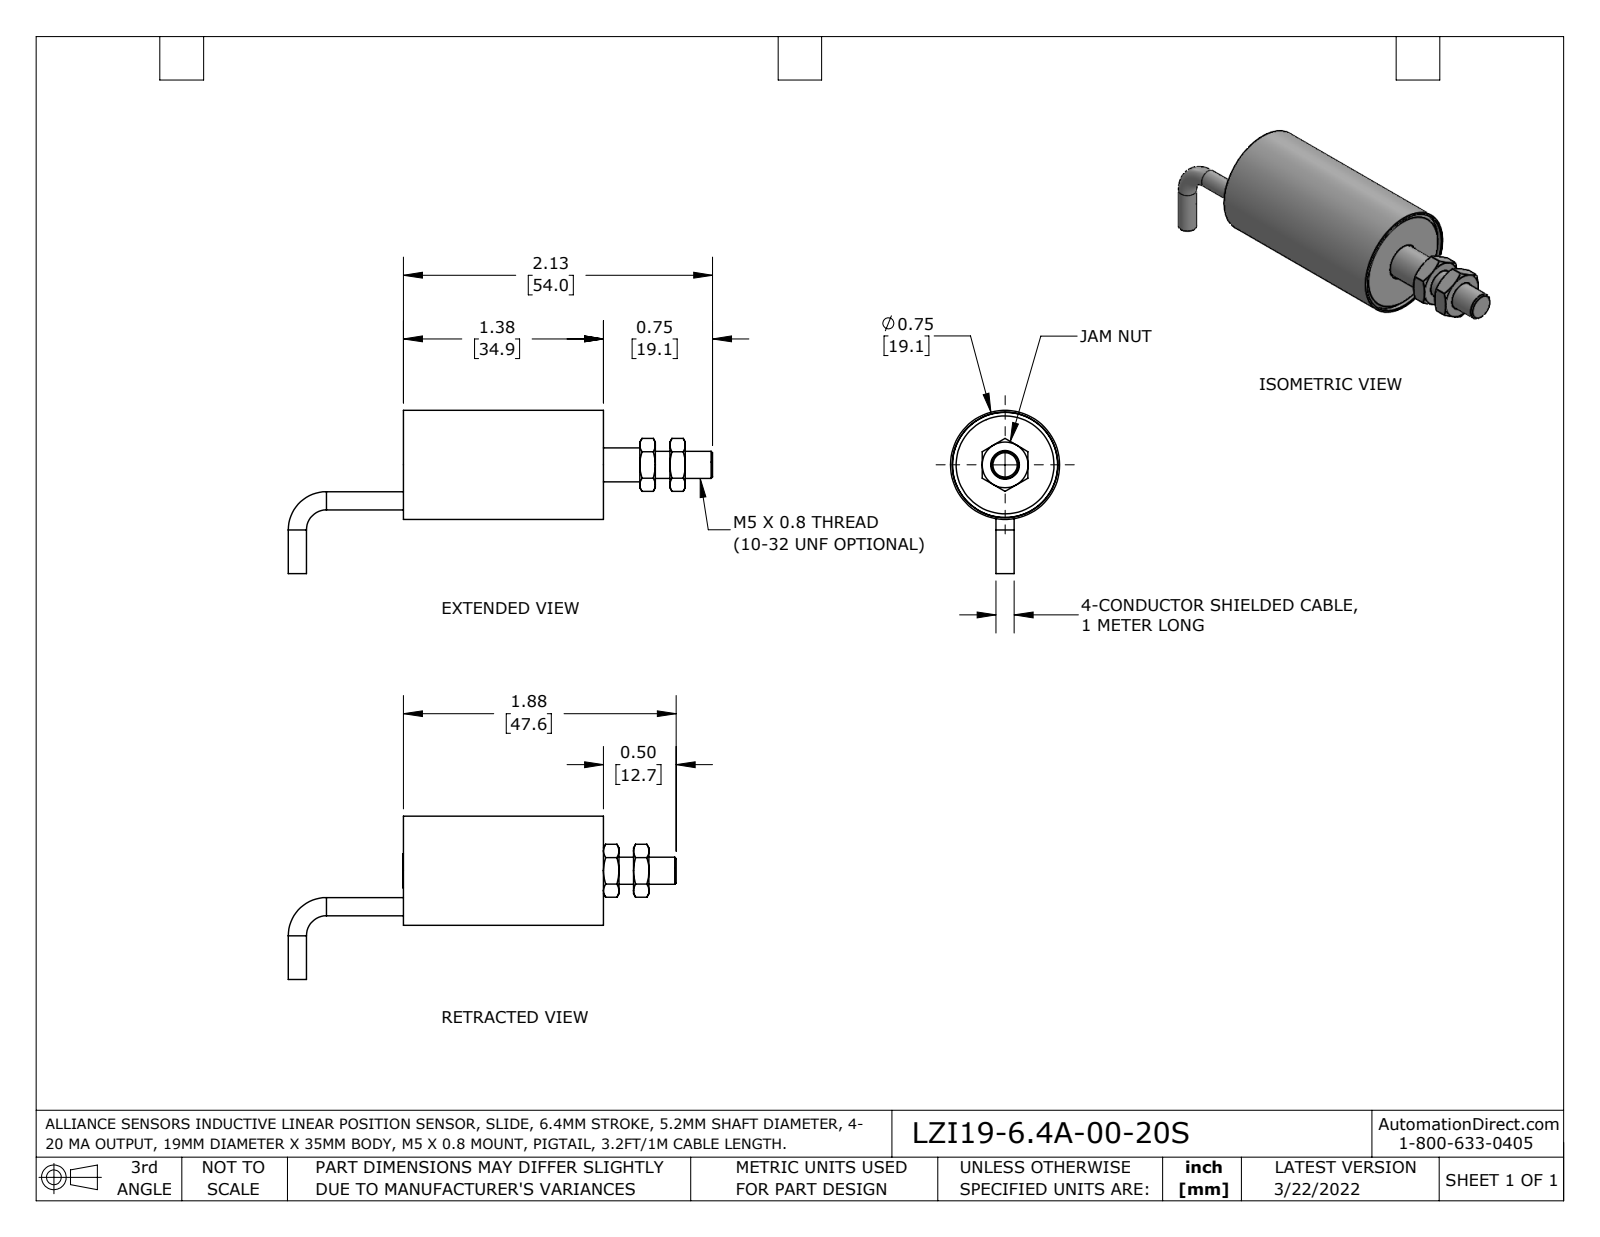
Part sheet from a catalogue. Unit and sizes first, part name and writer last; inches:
Units: inches
Overall size (bounding box): 2.918 × 1.121 × 0.75
Round holes (diameter × count): ⌀0.165 ×1, ⌀0.188 ×1, ⌀0.197 ×1, ⌀0.234 ×1, ⌀0.281 ×1, ⌀0.68 ×1, ⌀0.725 ×1
Round bosses / shafts (diameter × count): ⌀0.125 ×2, ⌀0.75 ×1, ⌀0.723 ×1, ⌀0.278 ×1, ⌀0.187 ×1
Partial cylindrical surfaces — rounded edges, fillets, slot ends (radius × count): R0.052 ×1
Main face-to-face distances: 0.06, 1.295, 0.08, 1.235, 1.355, 0.315, 0.206, 0.106, 0.374, 0.1
Volume: 0.3 in³ · Surface area: 15.45 in²
Bodies: 10 solids, 137 faces (42 planar, 44 cylindrical, 51 other)
Part name (STEP PRODUCT): 3100-0076_B18.2.4.5M - Hex jam nut, M5 x 0.8 --D-N; 3120-0007-ZY; LZI19-6.4A-00-20S; 3300-0008-06_-01 (+6 more)
STEP written by: SolidWorks 2021 (AUTOMOTIVE_DESIGN)
